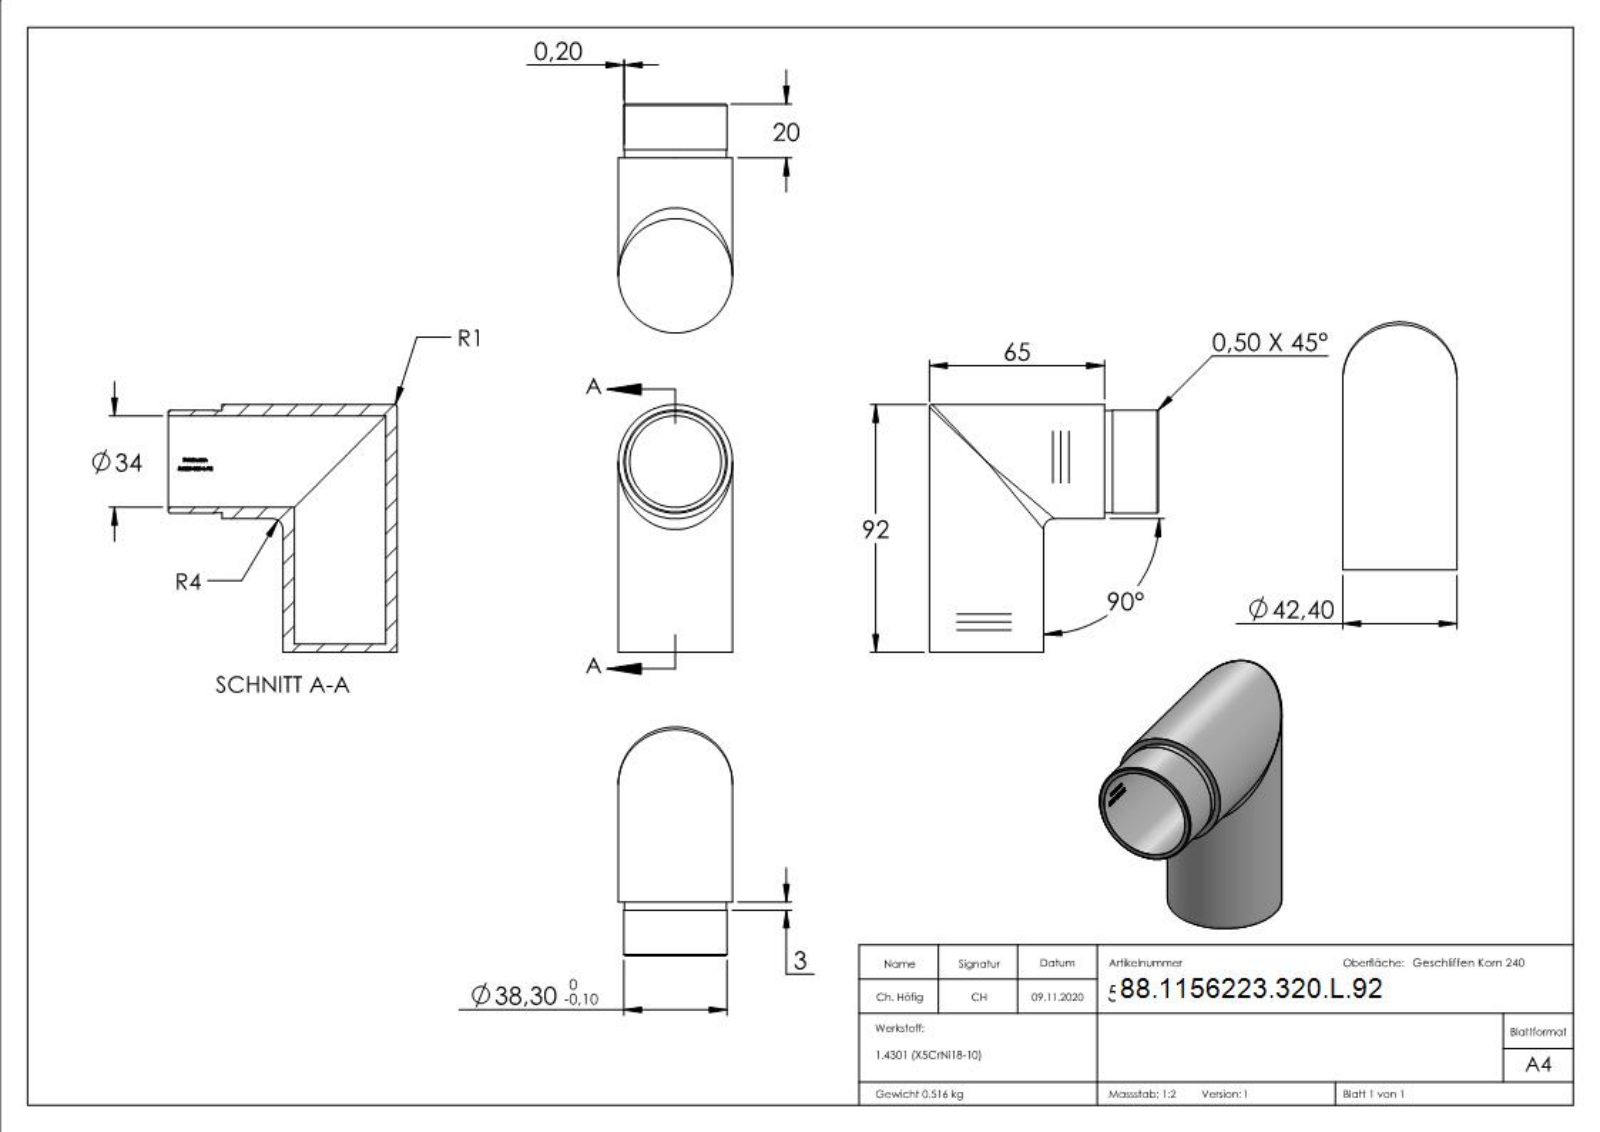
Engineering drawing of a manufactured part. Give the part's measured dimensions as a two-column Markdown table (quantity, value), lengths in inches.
| quantity | value |
| --- | --- |
| part name | 56223-320-L-92 |
| STEP written by | SolidWorks 2018 (CONFIG_CONTROL_DESIGN) |
| units | inches |
| bodies | 1 solid, 298 faces (119 planar, 40 cylindrical, 139 other) |
| overall size | 3.622 × 3.346 × 1.669 |
| volume | 3.989 in³ |
| surface area | 53.51 in² |
| round holes (diameter × count) | 1.339 × 2 |
| round bosses / shafts (diameter × count) | 1.669 × 2, 1.508 × 1, 1.492 × 1 |
| partial cylindrical surfaces (radius × count) | 0.673 × 1 |
| main face-to-face distances | 0.118, 0.787, 0.669, 2.661, 2.543, 0.017, 0.117, 2.667, 2.548, 0.015 |
